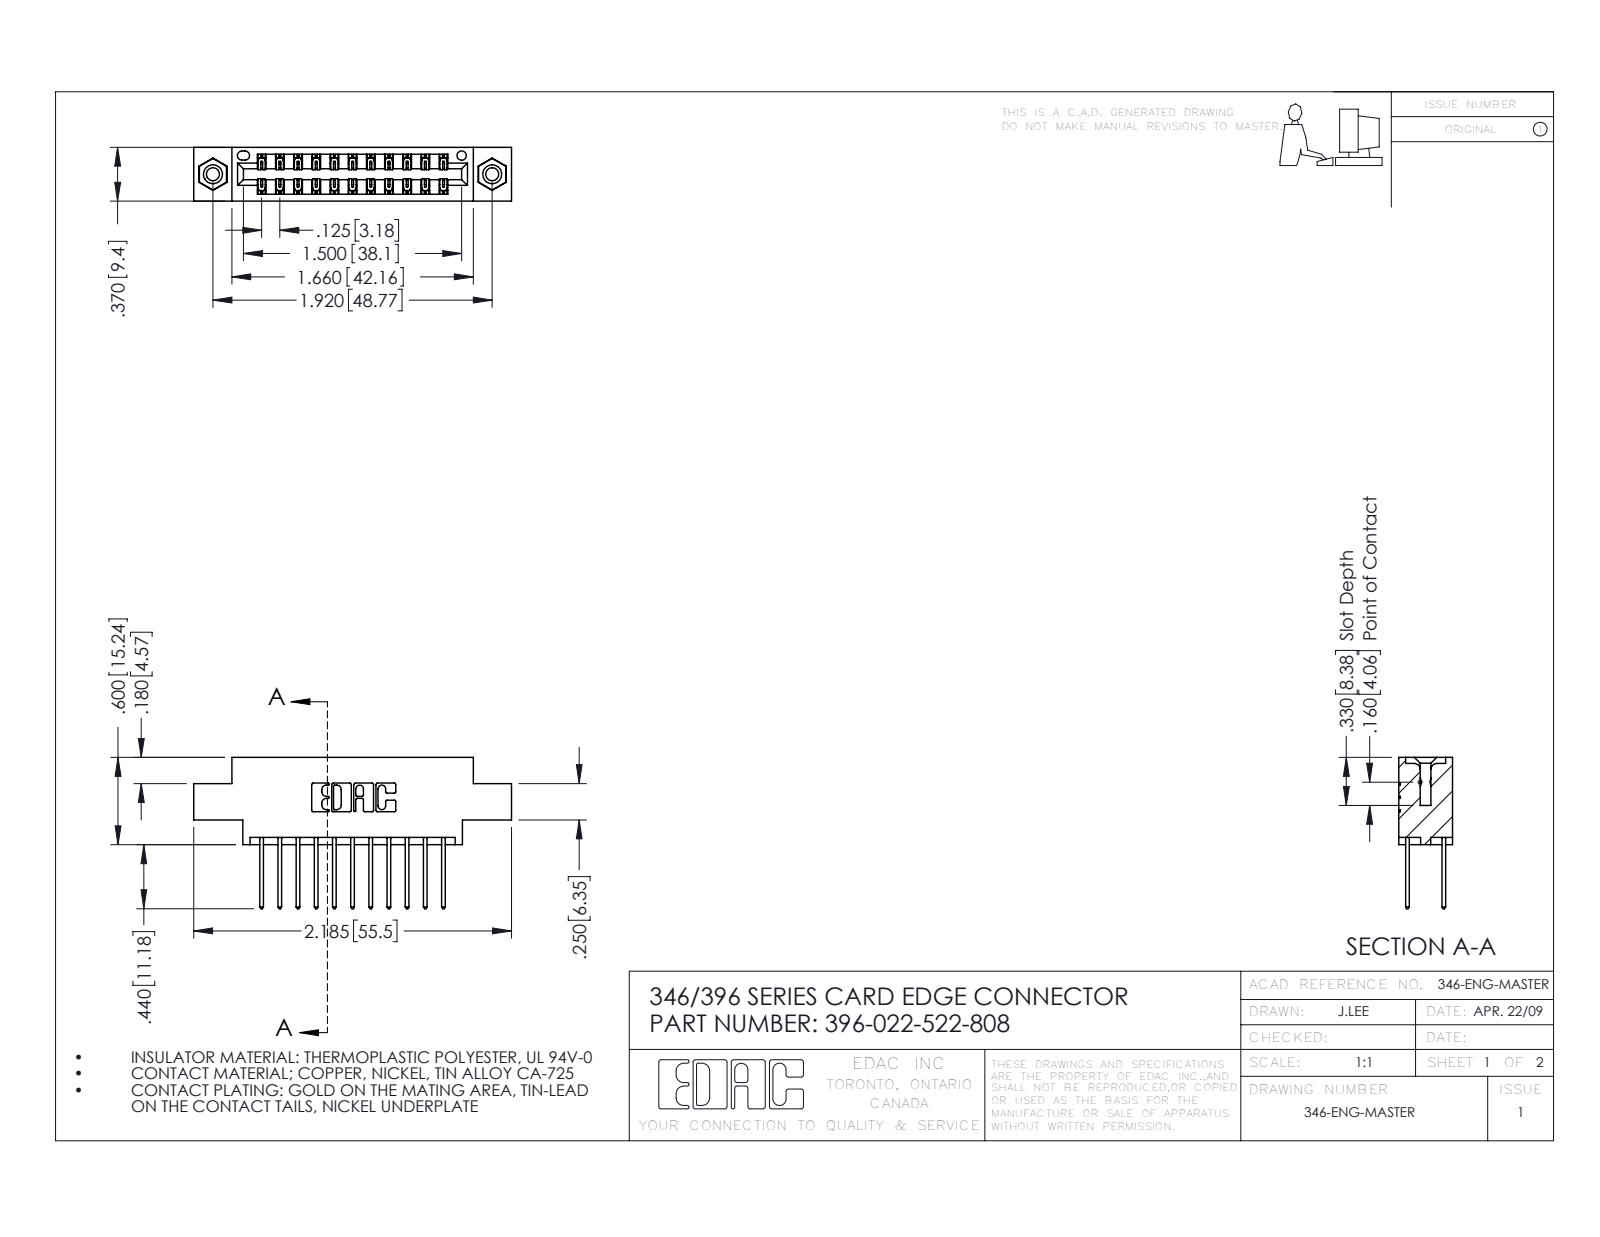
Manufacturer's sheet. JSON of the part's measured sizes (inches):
{"part_name": "346 Part_0.170 Offset - 0.156 Dia-TI; 345-292-001_345-293-122; 396-022-522-808; 345-250-001_345-250-003-102", "step_written_by": "SolidWorks 2016 (CONFIG_CONTROL_DESIGN)", "units": "inches", "bodies": {"solids": 25, "faces": 1330, "planar": 882, "cylindrical": 432, "other": 16}, "overall_size": [2.185, 1.04, 0.37], "volume_in3": 0.309, "surface_area_in2": 10.75, "round_holes": [[0.089, 2], [0.125, 2], [0.156, 2], [0.064, 1]], "round_bosses_or_shafts": [[0.155, 2]], "partial_cylinders_radius": [[0.006, 33], [0.01, 22], [0.01, 22], [0.007, 6], [0.031, 6], [0.026, 3], [0.014, 2], [0.022, 2]], "face_to_face_distances": [0.25, 0.048, 0.322, 0.37, 0.072, 0.298, 0.025, 0.275, 0.222, 0.148], "hole_center_spacings": [0.246, 1.715, 1.92]}
